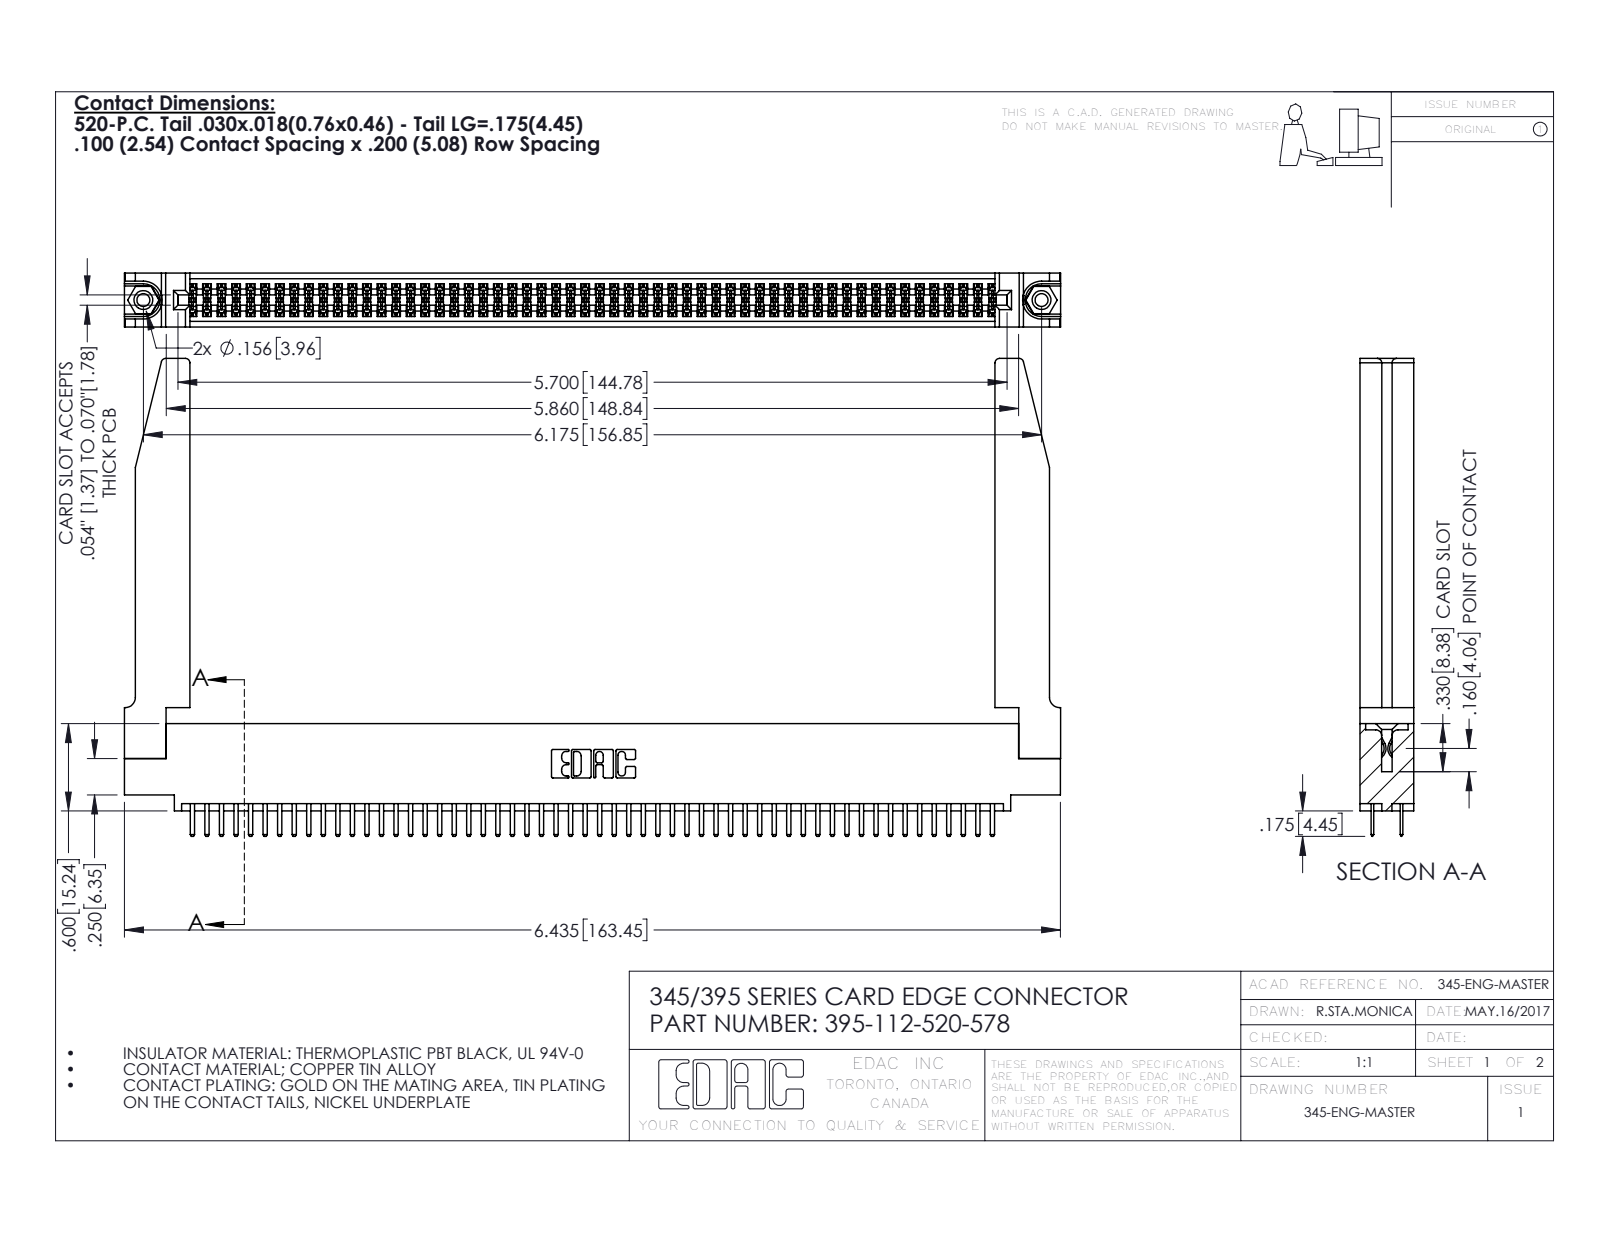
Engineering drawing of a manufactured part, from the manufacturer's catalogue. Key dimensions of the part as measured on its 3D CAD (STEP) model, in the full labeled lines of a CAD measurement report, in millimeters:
Part name (STEP PRODUCT): 345 Part_0.110 Offset - 0.156 Dia-TH; 345-250-001_345-250-001-102; 395-112-520-578; 345-292-001_345-293-120 (+1 more)
STEP written by: SolidWorks 2016 (CONFIG_CONTROL_DESIGN)
Units: millimetres
Bodies: 117 solids, 6412 faces (4146 planar, 2214 cylindrical, 52 other)
Overall size (bounding box): 163.5 × 83.4 × 9.4
Volume: 23 660 mm³ · Surface area: 30 580 mm²
Round holes (diameter × count): ⌀2.3 ×2, ⌀3.2 ×2, ⌀4 ×2, ⌀1.6 ×1
Round bosses / shafts (diameter × count): ⌀3.9 ×2
Partial cylindrical surfaces — rounded edges, fillets, slot ends (radius × count): R0.2 ×168, R0.3 ×116, R0.3 ×22, R0.8 ×8, R0.2 ×6, R0.8 ×6, R0.7 ×3, R0.4 ×2
Main face-to-face distances: 1.8, 9.4, 7.6, 5.1, 2.5, 6.9, 0.6, 5.7, 0.6, 1.8
Hole centre spacings: 6.9, 150.9, 156.8
